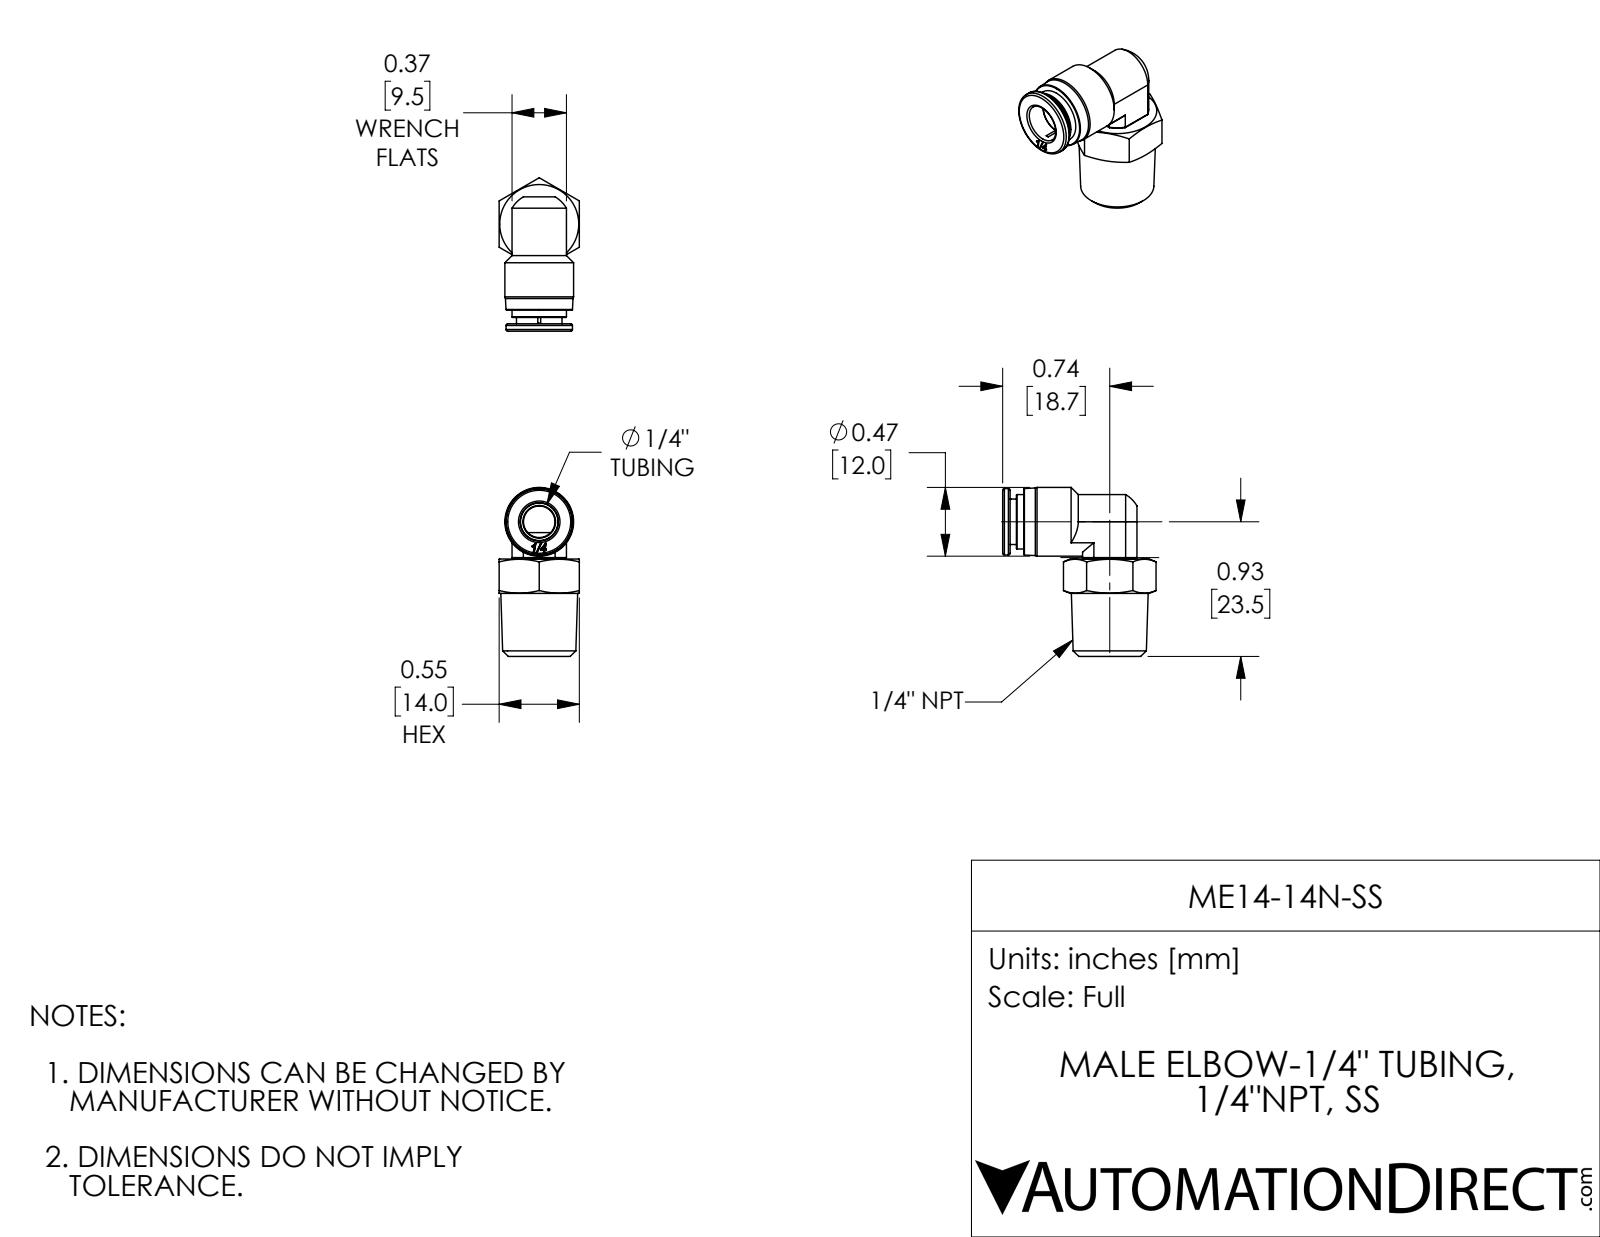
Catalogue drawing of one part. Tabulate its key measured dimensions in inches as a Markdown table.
| quantity | value |
| --- | --- |
| part name | ME14-14N-SS |
| STEP written by | SolidWorks 2017 (AUTOMOTIVE_DESIGN) |
| units | inches |
| bodies | 2 solids, 134 faces (55 planar, 33 cylindrical, 46 other) |
| overall size | 1.161 × 1.054 × 0.551 |
| volume | 0.232 in³ |
| surface area | 4.819 in² |
| round holes (diameter × count) | 0.157 × 1, 0.217 × 1, 0.238 × 1, 0.258 × 1, 0.262 × 1, 0.319 × 1 |
| round bosses / shafts (diameter × count) | 0.472 × 1, 0.457 × 1, 0.374 × 1, 0.313 × 1, 0.236 × 1 |
| partial cylindrical surfaces (radius × count) | 0.008 × 4, 0.217 × 1 |
| main face-to-face distances | 0.551, 0.089, 0.463, 0.669, 0.374, 0.051, 0.671, 0.923, 0.872, 0.094 |
